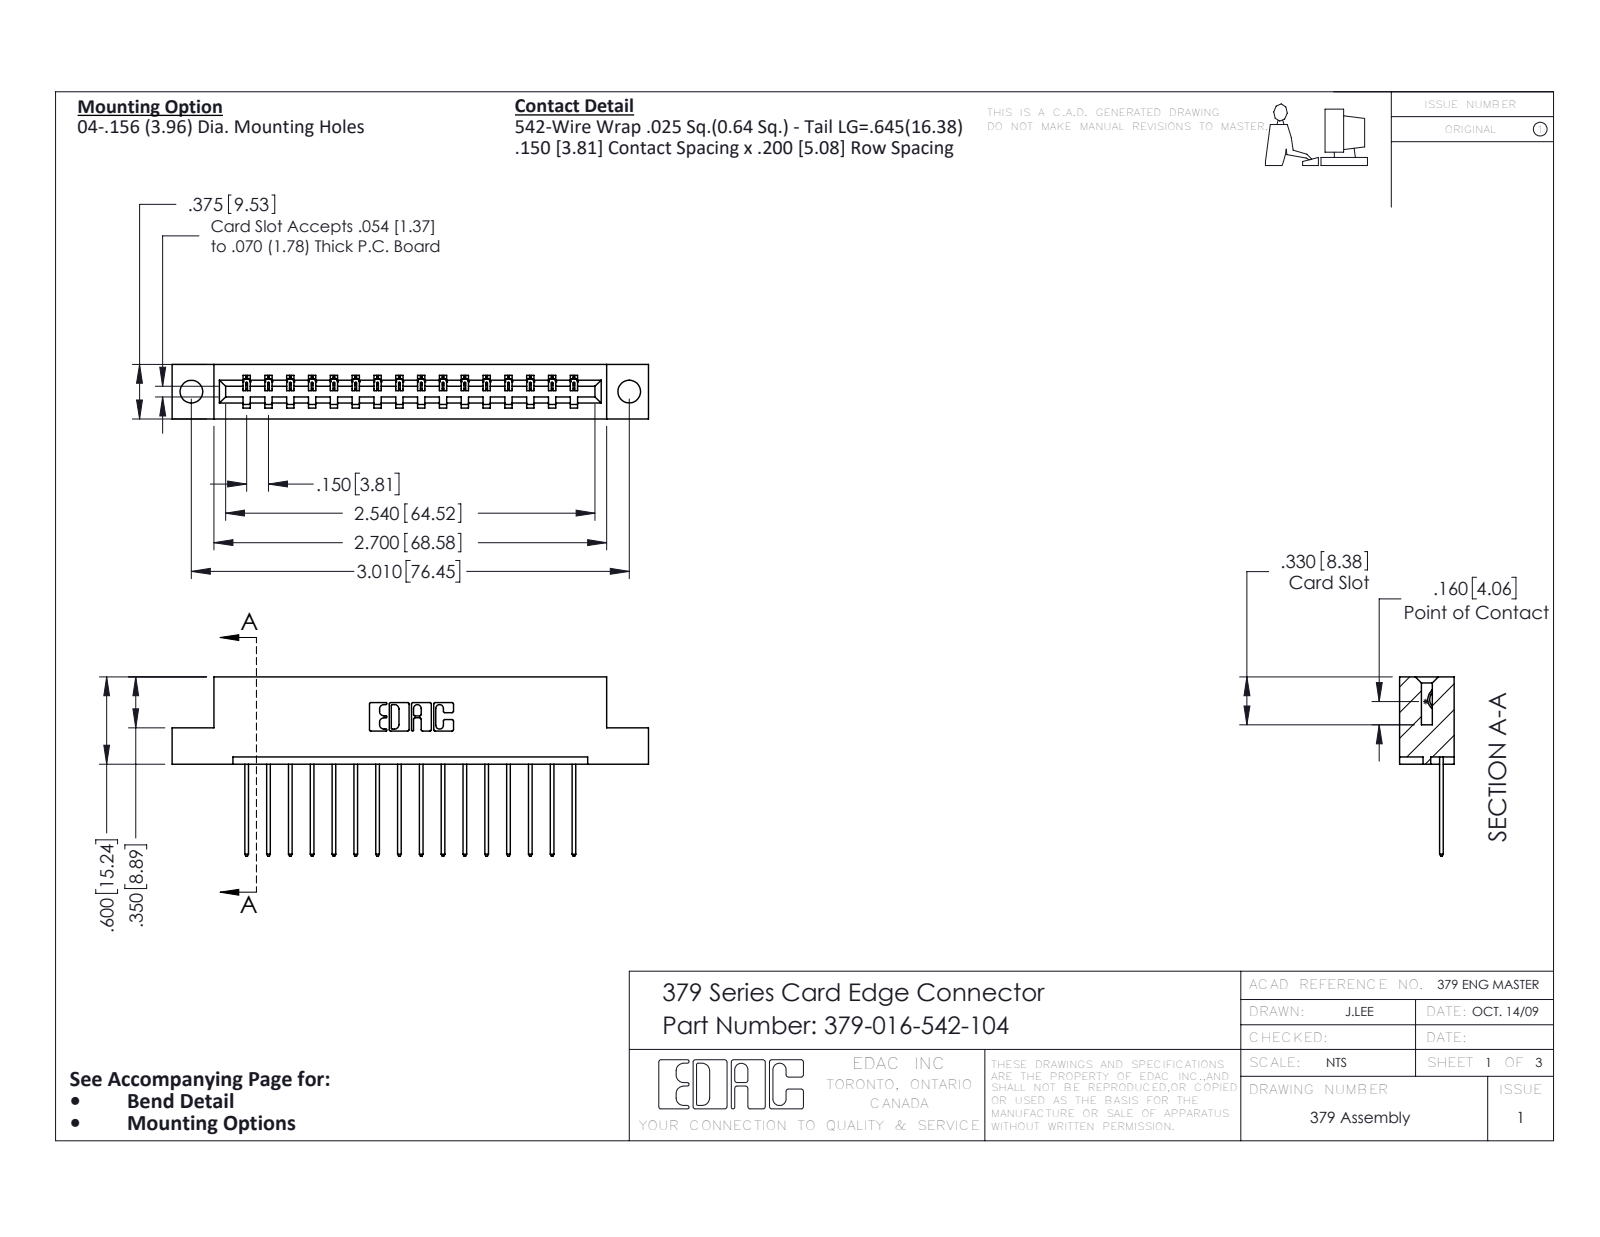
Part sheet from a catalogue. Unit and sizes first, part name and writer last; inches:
Units: inches
Overall size (bounding box): 3.275 × 1.232 × 0.375
Round holes (diameter × count): ⌀0.156 ×2
Partial cylindrical surfaces — rounded edges, fillets, slot ends (radius × count): R0.006 ×32, R0.01 ×32, R0.01 ×22, R0.007 ×6, R0.031 ×6, R0.026 ×3, R0.014 ×1, R0.022 ×1
Main face-to-face distances: 0.3, 0.075, 0.375, 0.6, 0.15, 0.225, 0.45, 0.2, 0.275, 0.1
Hole centre spacings: 3.01
Volume: 0.511 in³ · Surface area: 13.13 in²
Bodies: 17 solids, 1042 faces (742 planar, 300 cylindrical, 0 other)
Part name (STEP PRODUCT): 379 Part_Flush - .156 Dia - TH; 345-292-001_345-293-142; 379-016-542-104
STEP written by: SolidWorks 2020 (CONFIG_CONTROL_DESIGN)
